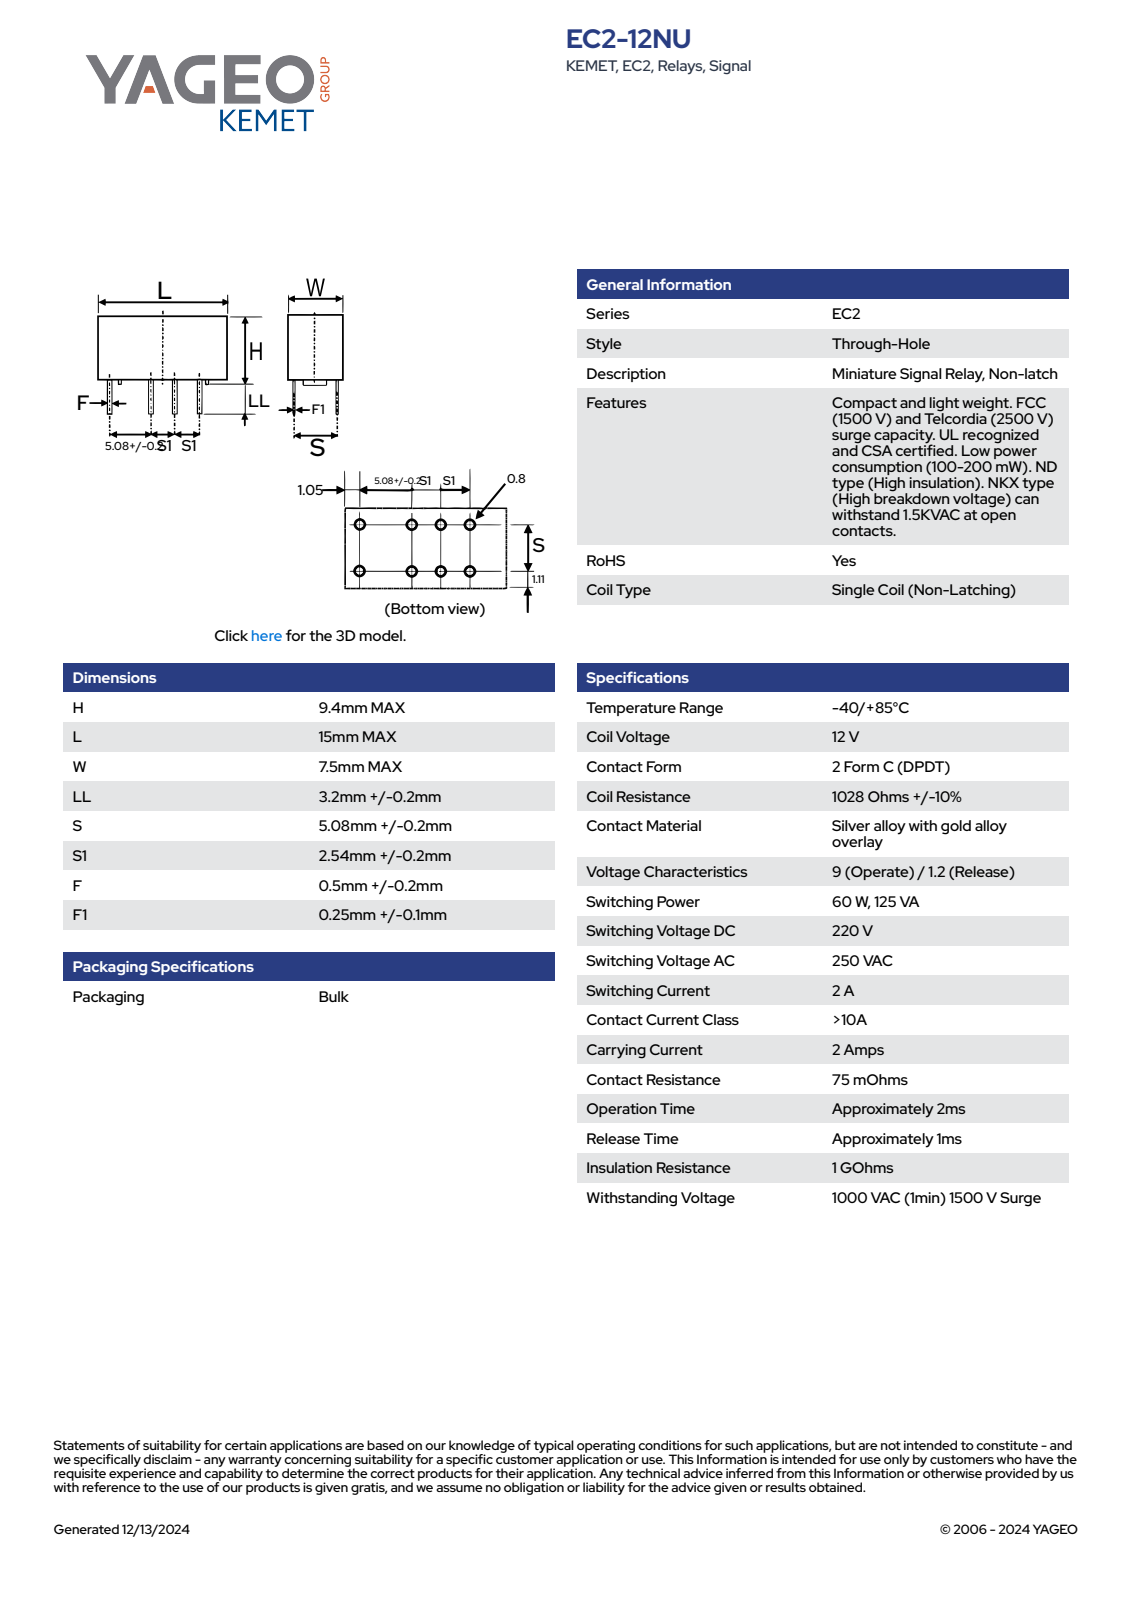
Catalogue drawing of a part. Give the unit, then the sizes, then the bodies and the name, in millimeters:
Units: millimetres
Overall size (bounding box): 15 × 12.8 × 7.5
Main face-to-face distances: 7.5, 8.9, 15, 5.08, 6.42, 0.5, 1.08, 1.33, 6.17, 2.54
Volume: 1 006 mm³ · Surface area: 680 mm²
Bodies: 1 solid, 110 faces (110 planar, 0 cylindrical, 0 other)
Part name (STEP PRODUCT): IR_TEC2S_L15W7.5H9.4
STEP written by: SolidWorks 2014 (AUTOMOTIVE_DESIGN)
